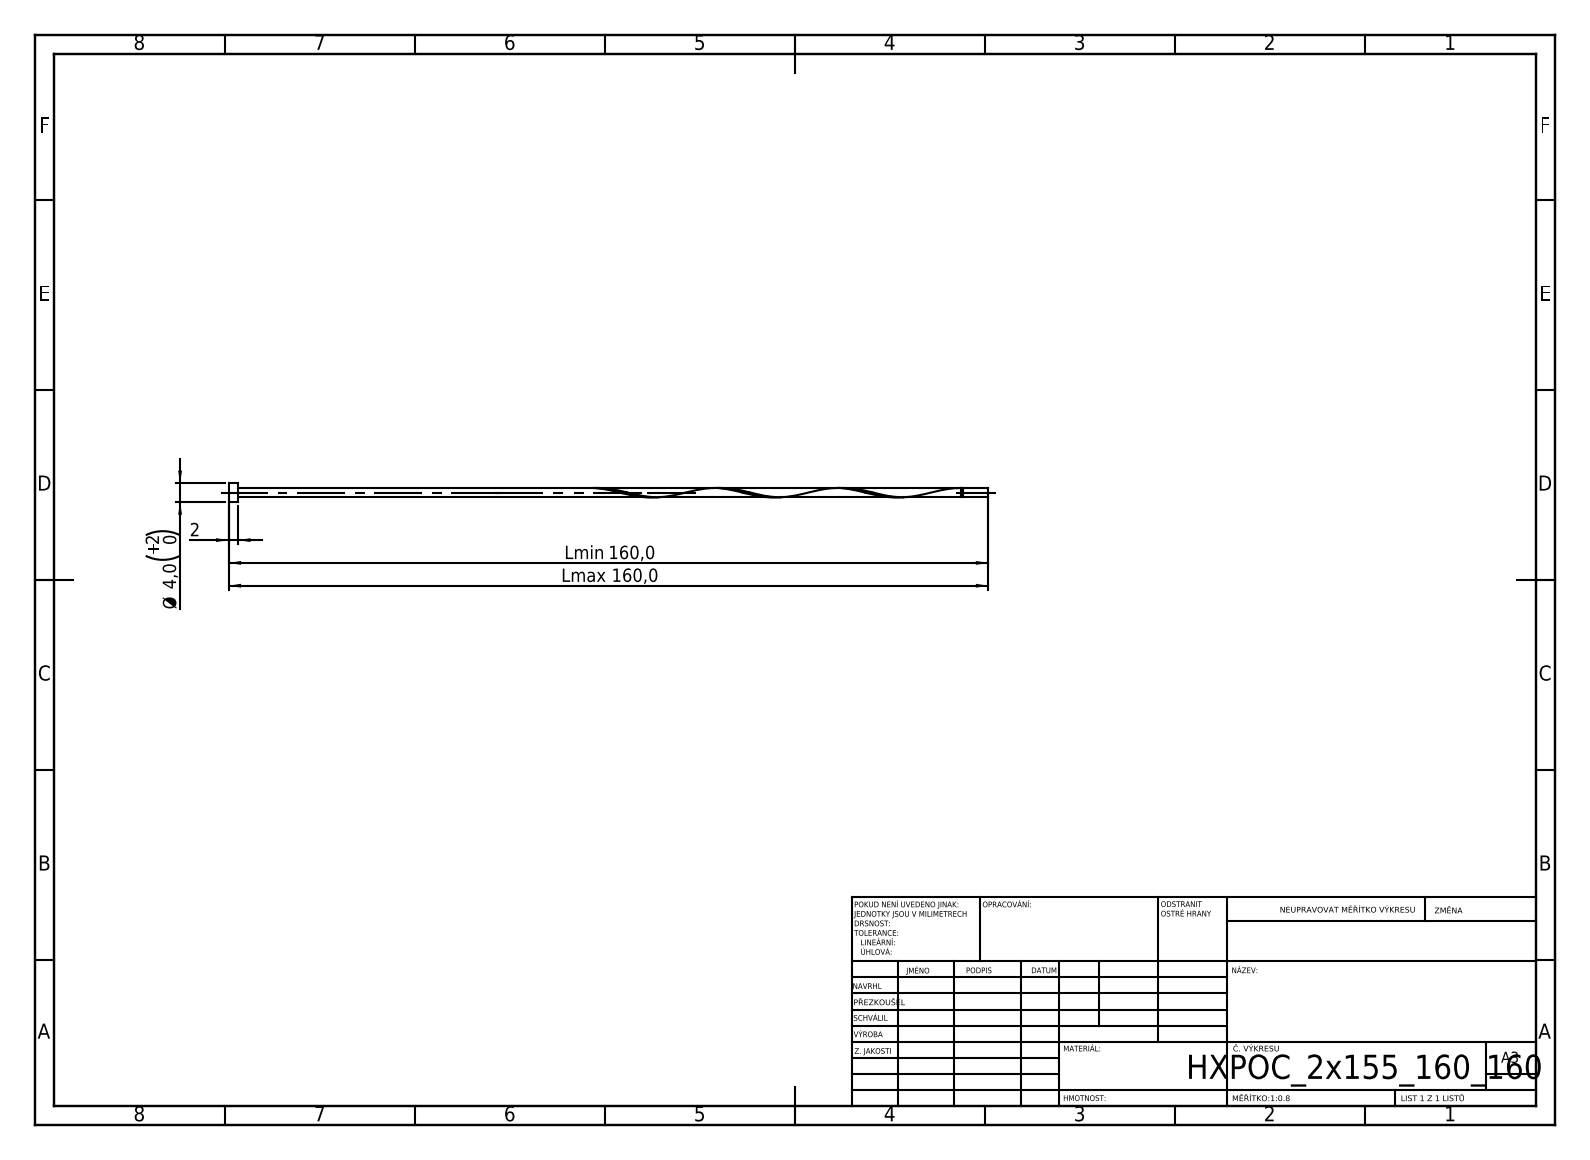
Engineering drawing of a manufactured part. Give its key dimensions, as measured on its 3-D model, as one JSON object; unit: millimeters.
{"step_written_by": "SolidWorks 2019 (CONFIG_CONTROL_DESIGN)", "units": "millimeters", "bodies": {"solids": 1, "faces": 16, "planar": 6, "cylindrical": 9, "other": 1}, "overall_size": [160, 4, 4], "volume_mm3": 625, "surface_area_mm2": 1384, "round_bosses_or_shafts": [[4, 1], [2, 1], [1.6, 1]], "face_to_face_distances": [2, 160, 158, 154.72, 152.72, 5.28, 154.32, 152.32, 0.4, 5.68]}
